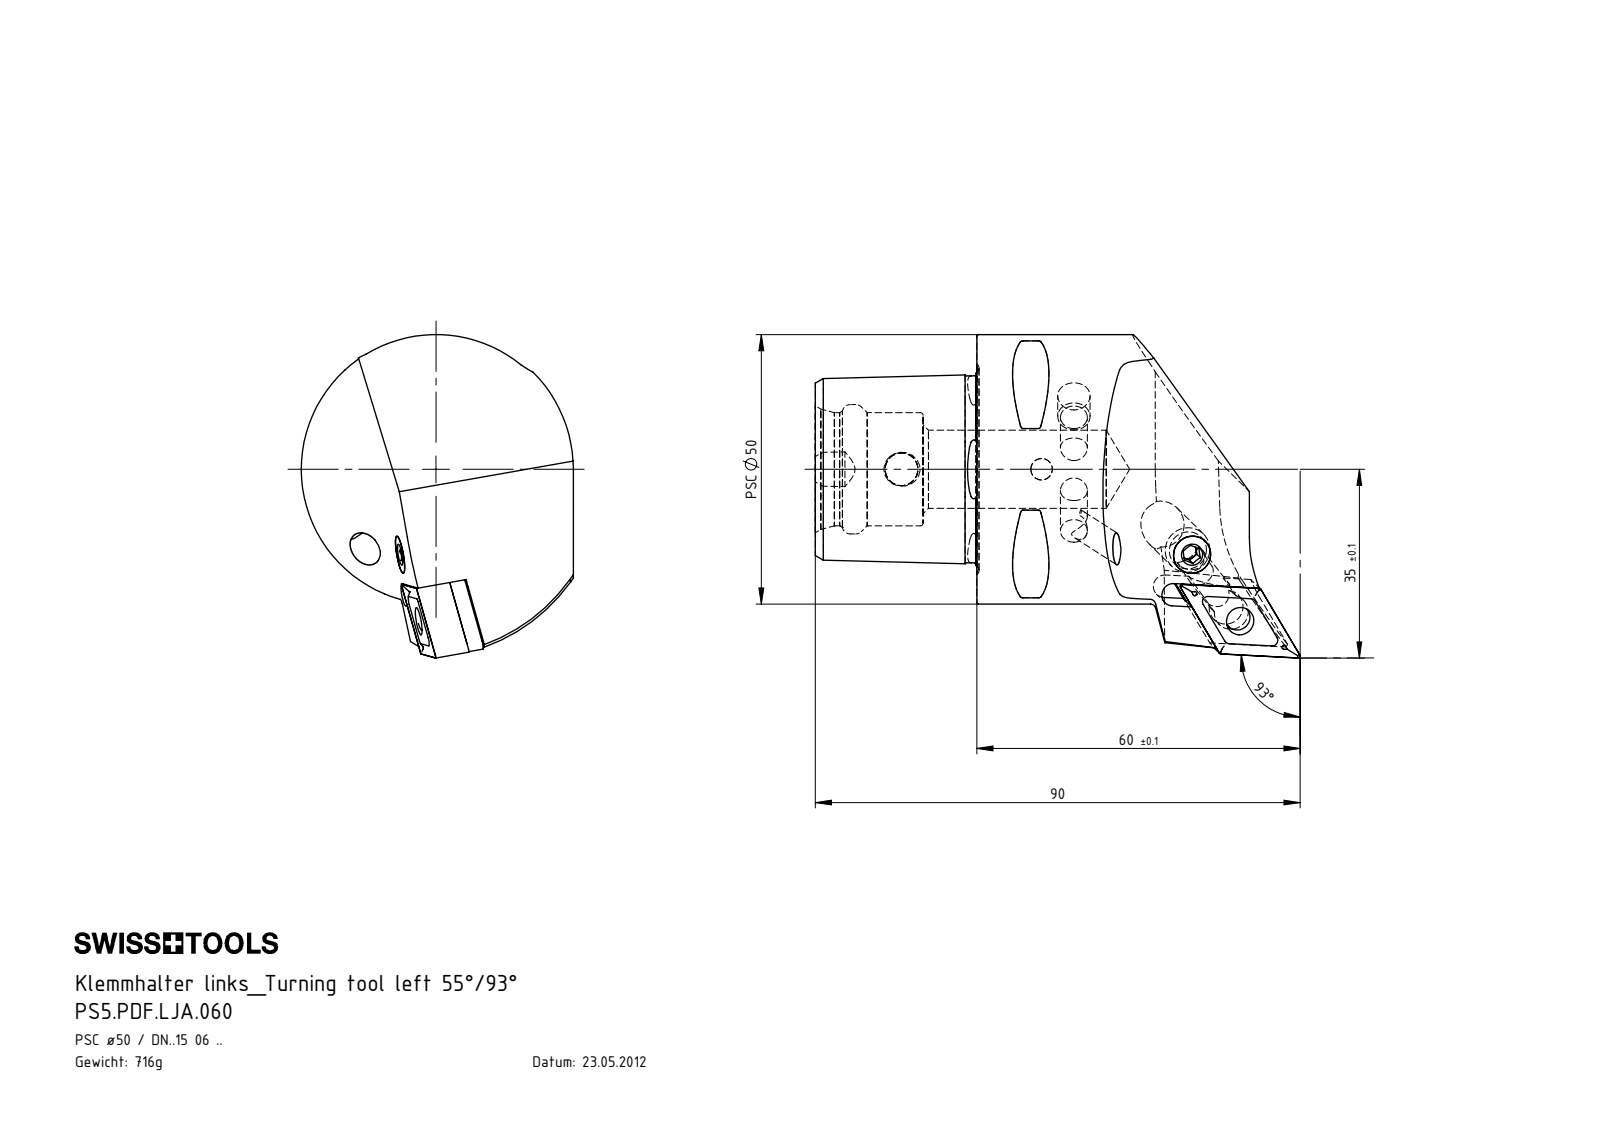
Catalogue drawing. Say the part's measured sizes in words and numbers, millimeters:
The part is named "PS5-PDF.LJA.060; KVT_MB_600_060; WCD-ER1.101.000; DNMG150604 (+4 more)". Its 3-D file was written by "SolidWorks 2012 (CONFIG_CONTROL_DESIGN)". It is 8 solids with 339 faces: 90 planar, 84 cylindrical and 165 other. Overall it measures 90 by 60 by 50.5 millimeters. Its volume is 92 114 cubic millimeters and its surface area 22 207 square millimeters. Round holes: 3 of diameter 5, 1 of diameter 4, 1 of diameter 5.16, 1 of diameter 6, 1 of diameter 6.1, 1 of diameter 6.4, 1 of diameter 7, 1 of diameter 8.4, 1 of diameter 14.5, 1 of diameter 21, 1 of diameter 24. Round bosses or shafts: 1 of diameter 50, 1 of diameter 8, 1 of diameter 7.9, 1 of diameter 6.4, 1 of diameter 6, 1 of diameter 4.7, 1 of diameter 3.55. Partial cylindrical surfaces (rounded edges, fillets, slot ends): 8 of radius 0.5, 4 of radius 0.4, 4 of radius 1, 2 of radius 2.5, 1 of radius 2.1, 1 of radius 2.35, 1 of radius 2.8, 1 of radius 3. The main face-to-face distances are 30, 6.05, 3.18, 9.23, 12.7, 12.71, 19.18, 44.4, 12.29, 0.41. The hole center spacings are 15.59, 26.
